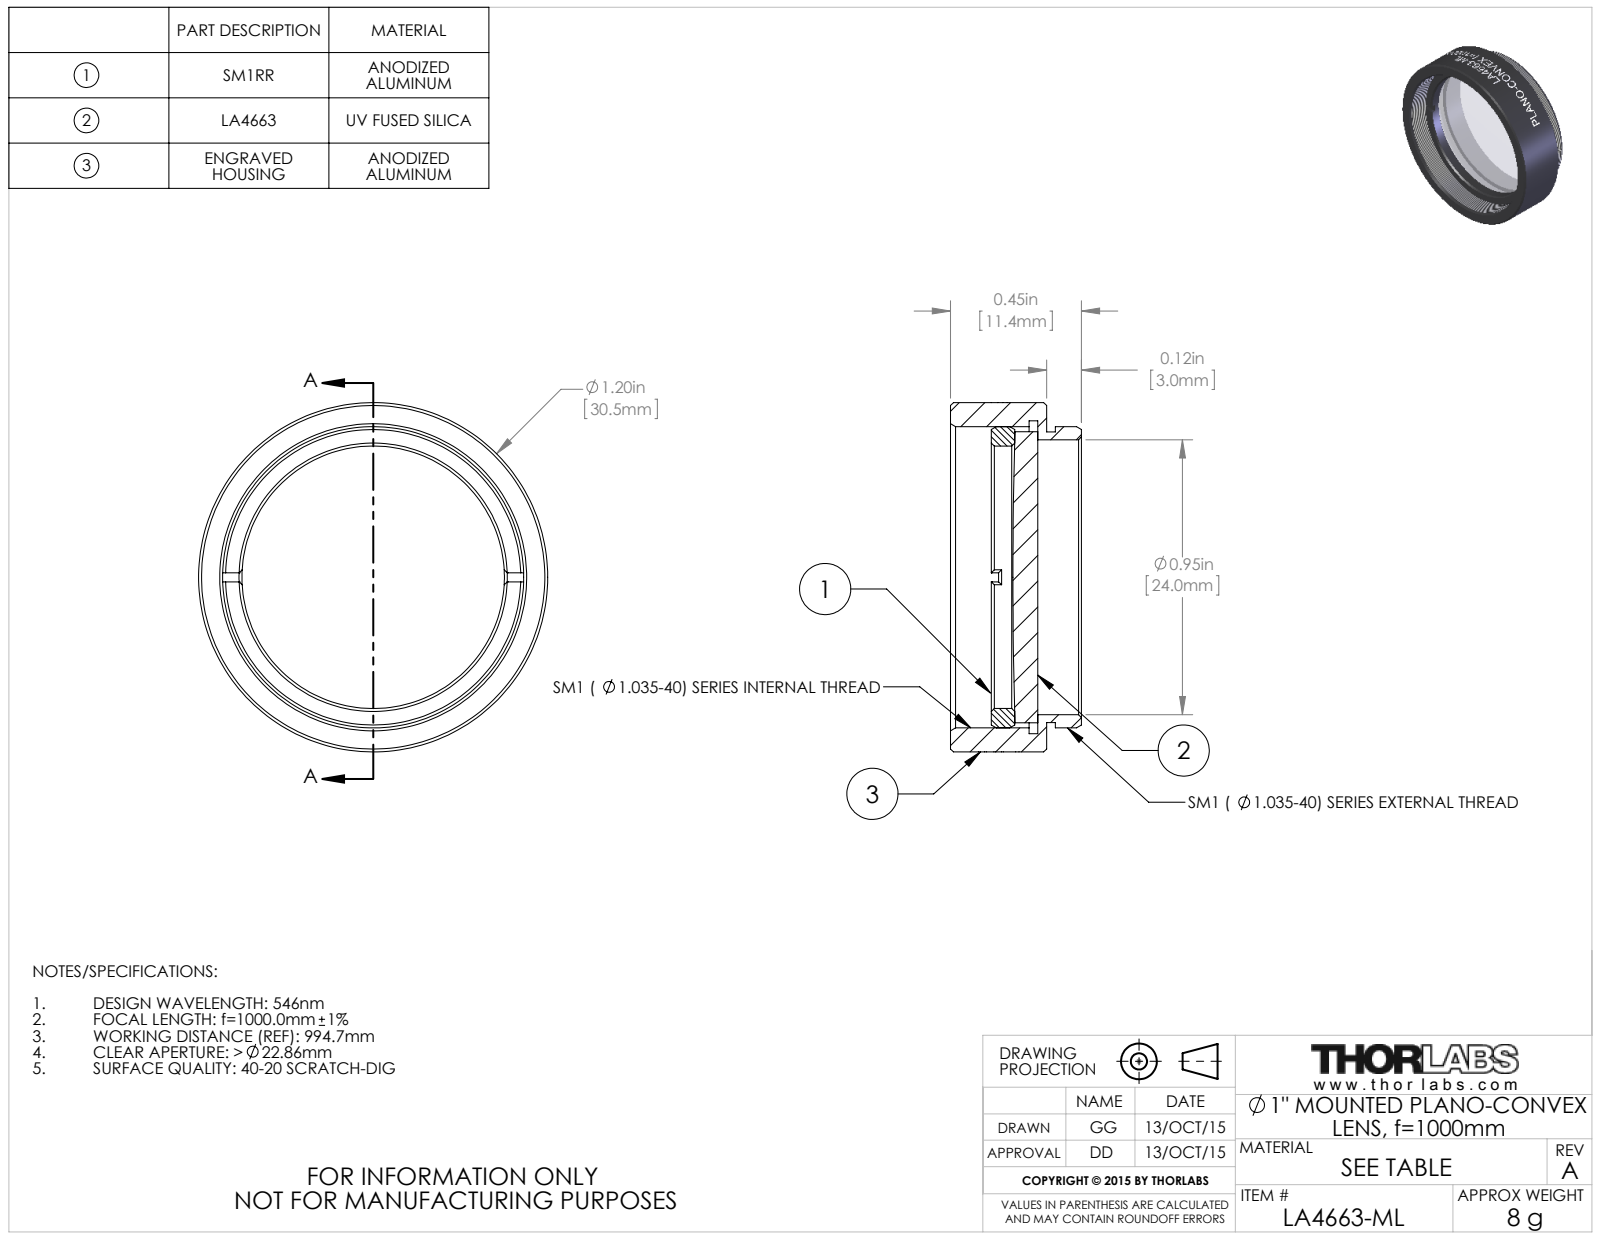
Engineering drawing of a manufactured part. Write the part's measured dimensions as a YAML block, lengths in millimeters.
part_name: "TTN039348-E0W"
step_written_by: "SolidWorks 2014 (CONFIG_CONTROL_DESIGN)"
units: millimeters
bodies: {solids: 3, faces: 125, planar: 20, cylindrical: 81, other: 24}
overall_size: [30.48, 30.48, 11.43]
volume: 3140
surface_area: 4313
round_holes:
  - {diameter: 22.91, count: 1}
  - {diameter: 24, count: 1}
  - {diameter: 26.29, count: 1}
  - {diameter: 27.31, count: 1}
round_bosses_or_shafts:
  - {diameter: 30.48, count: 1}
  - {diameter: 26.29, count: 1}
  - {diameter: 25.4, count: 1}
  - {diameter: 25.37, count: 1}
face_to_face_distances: [0.76, 2.03, 8.38, 7.62, 2.79, 5.59, 4.82, 4.06, 3.56, 2.29]
